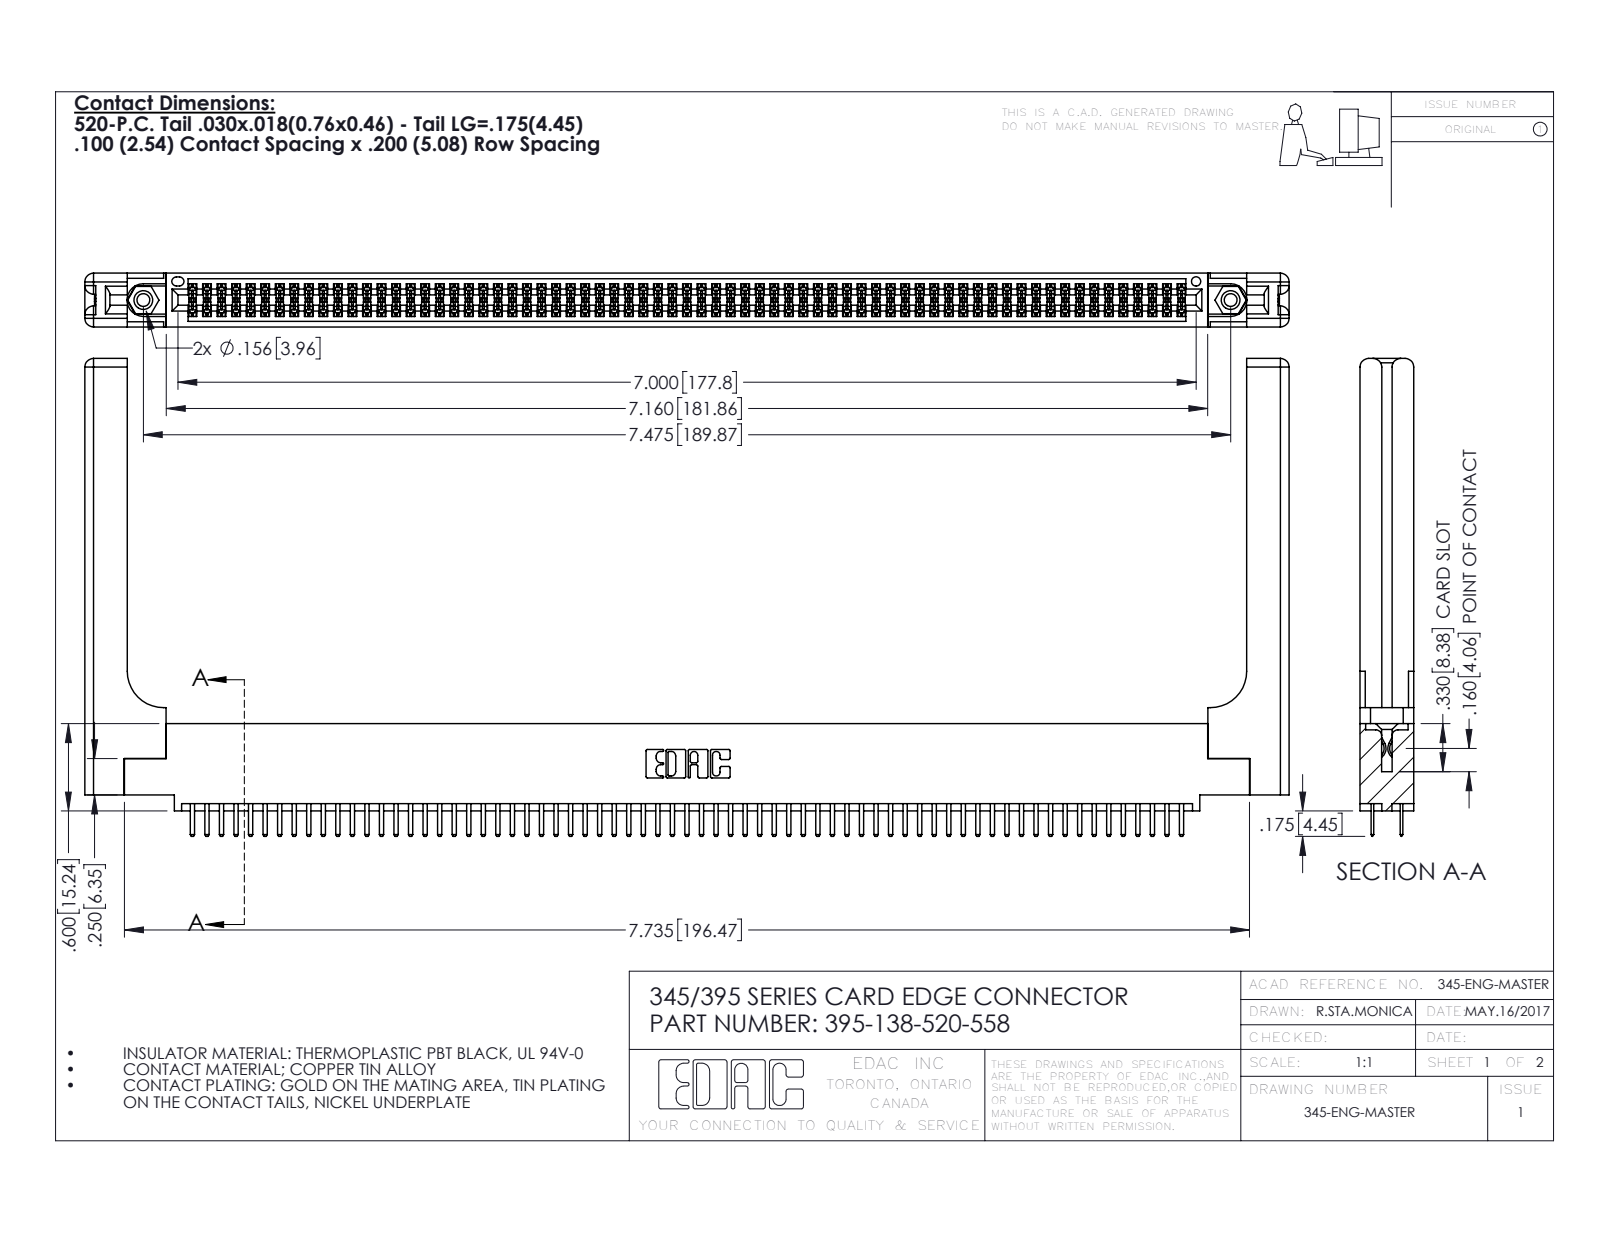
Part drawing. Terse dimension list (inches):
name: 345-292-001_345-293-120; 395-138-520-558; 345-220-058_345-220-058; 345-250-001_345-250-001-102 (+1 more)
written by: SolidWorks 2016 (CONFIG_CONTROL_DESIGN)
unit: in
bodies: 143 solids, 7838 faces (5062 planar, 2716 cylindrical, 60 other)
size: 8.279 × 3.285 × 0.37
volume: 1.771 in³; area: 55.67 in²
holes: 2× ⌀0.089, 2× ⌀0.125, 2× ⌀0.156, 1× ⌀0.064
bosses: 2× ⌀0.155
rounds: 207× R0.006, 142× R0.01, 22× R0.01, 16× R0.06, 6× R0.007, 6× R0.031, 3× R0.026, 2× R0.014
face distances: 0.072, 0.298, 0.37, 0.2, 0.098, 0.272, 0.025, 0.225, 0.022, 0.072
hole spacings: 0.27, 7.239, 7.475
